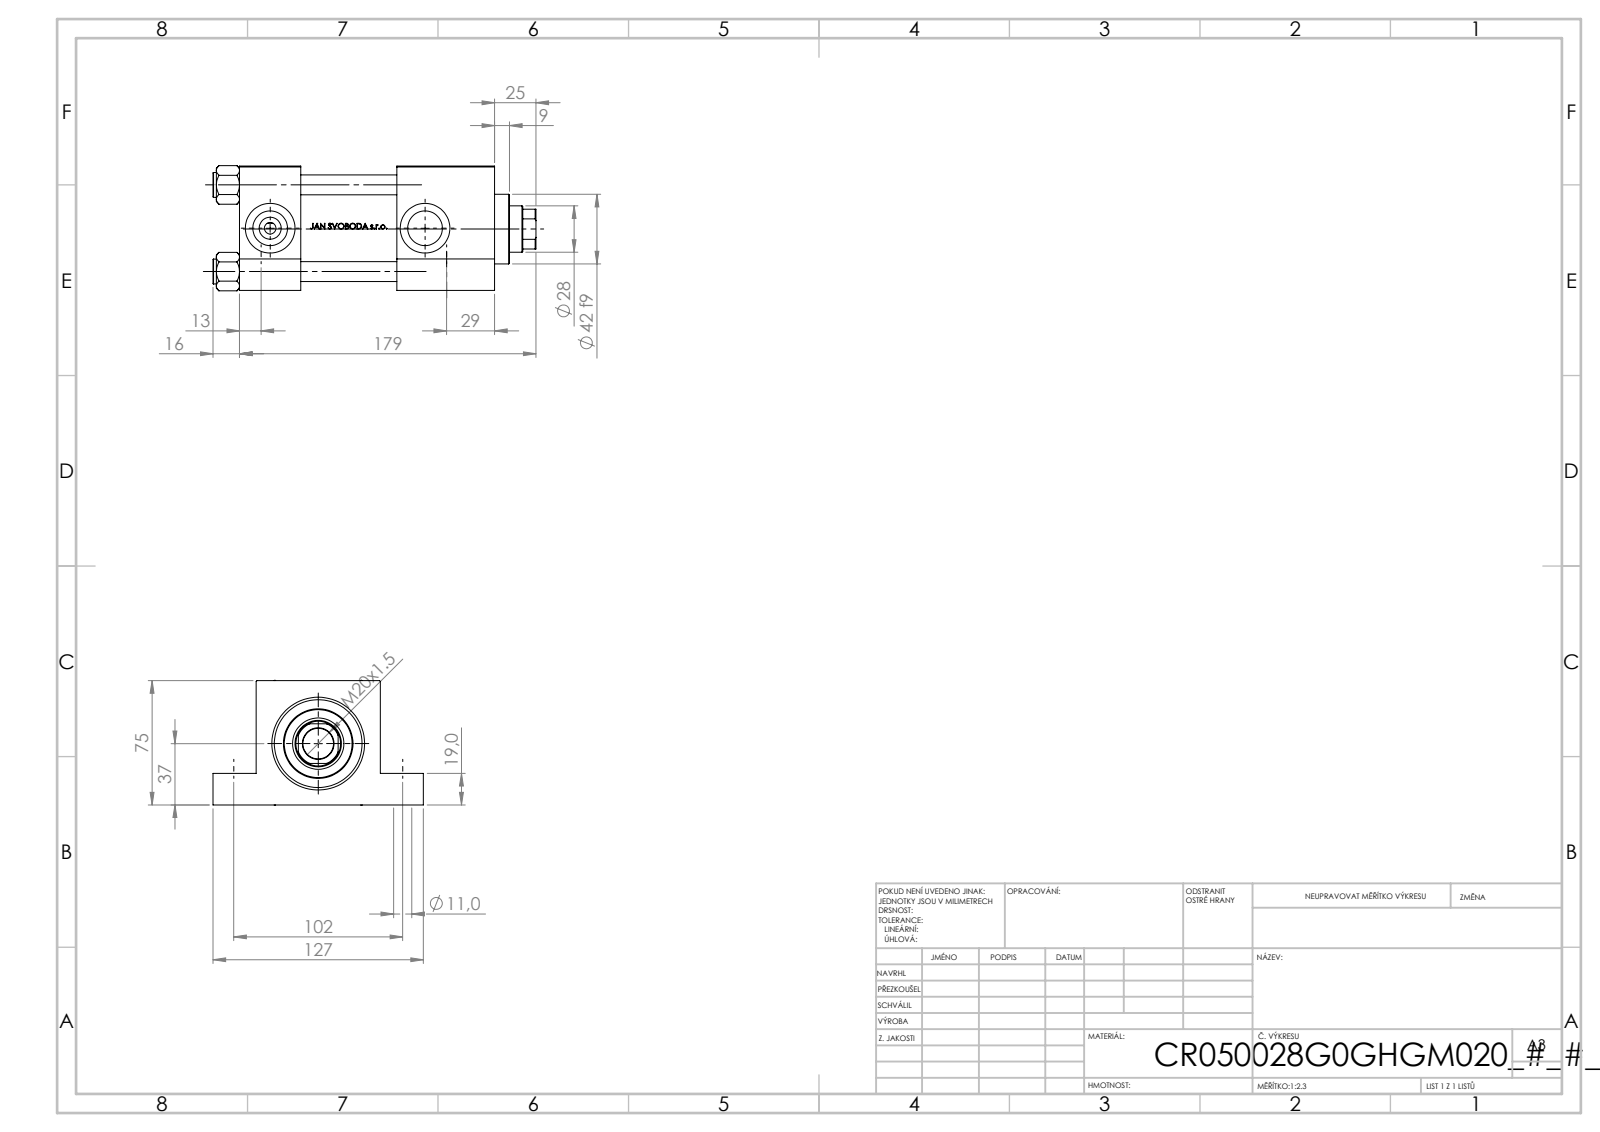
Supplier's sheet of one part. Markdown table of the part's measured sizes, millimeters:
| quantity | value |
| --- | --- |
| part name | V215CR_G_Body; V215CR_VCP_G; NUT_M5_G; V215_VC_A (+1 more) |
| STEP written by | SolidWorks 2019 (CONFIG_CONTROL_DESIGN) |
| units | millimeters |
| bodies | 15 solids, 1169 faces (452 planar, 137 cylindrical, 580 other) |
| overall size | 195 × 127 × 75.54 |
| volume | 798 345 mm³ |
| surface area | 177 095 mm² |
| round holes (diameter × count) | 12 × 4, 14 × 4, 7 × 2, 20.96 × 2, 30 × 2, 18.5 × 1, 28 × 1, 31 × 1, 41 × 1, 50 × 1, 53 × 1 |
| round bosses / shafts (diameter × count) | 15 × 4, 56 × 1, 42 × 1 |
| partial cylindrical surfaces (radius × count) | 13.5 × 1 |
| main face-to-face distances | 75, 37, 154, 117, 19, 56, 95, 58, 59, 26 |
| hole center spacings | 36.98, 52.3, 73.96, 102, 112, 151.49, 93.5 |
